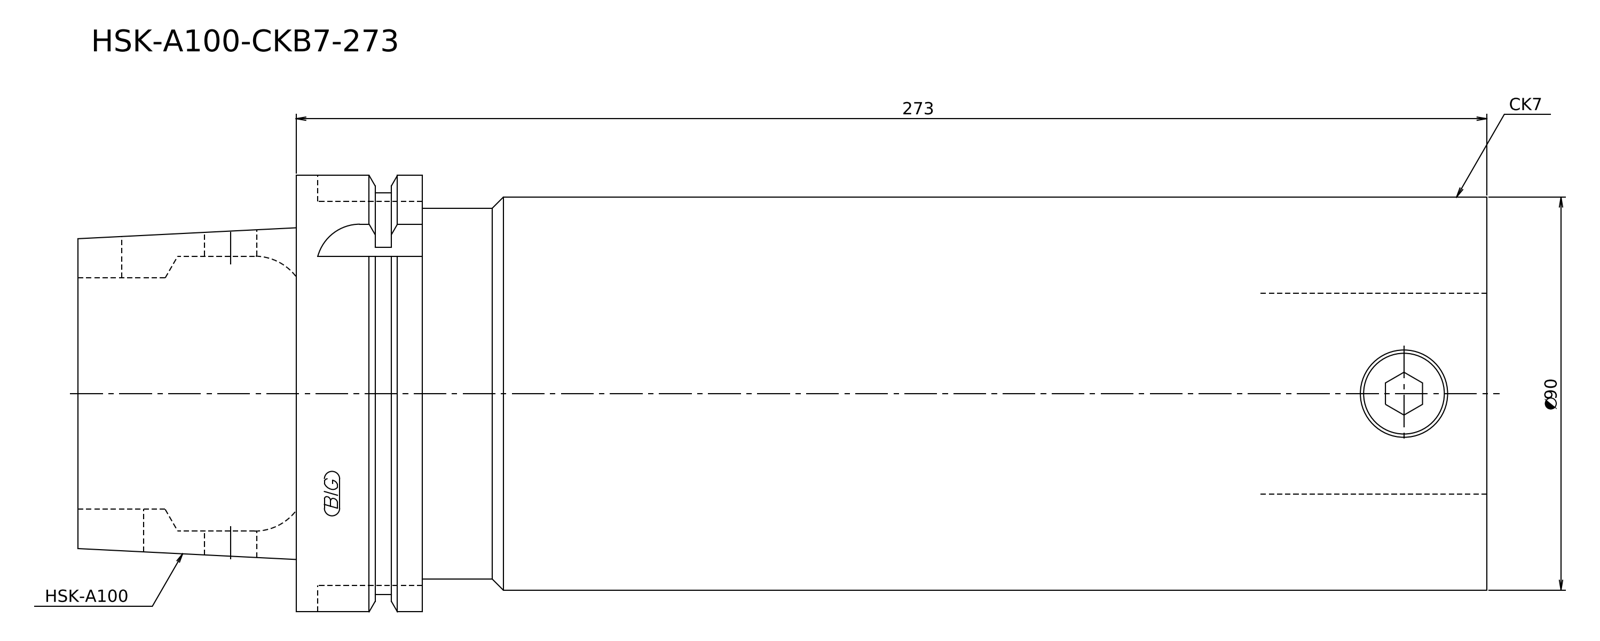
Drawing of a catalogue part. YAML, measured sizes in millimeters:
step_written_by: "Kubotek KeyCreator V8.5.1 (14335) (CONFIG_CONTROL_DESIGN)"
units: millimeters
bodies: {solids: 1, faces: 16, planar: 6, cylindrical: 6, other: 4}
overall_size: [323, 100, 100]
volume: 1975000
surface_area: 107196
round_bosses_or_shafts:
  - {diameter: 100, count: 1}
  - {diameter: 92, count: 1}
  - {diameter: 90, count: 1}
  - {diameter: 85, count: 1}
  - {diameter: 75.8, count: 1}
face_to_face_distances: [323, 273, 50, 244, 29, 79, 251.12, 7.12, 21.88, 71.88]
